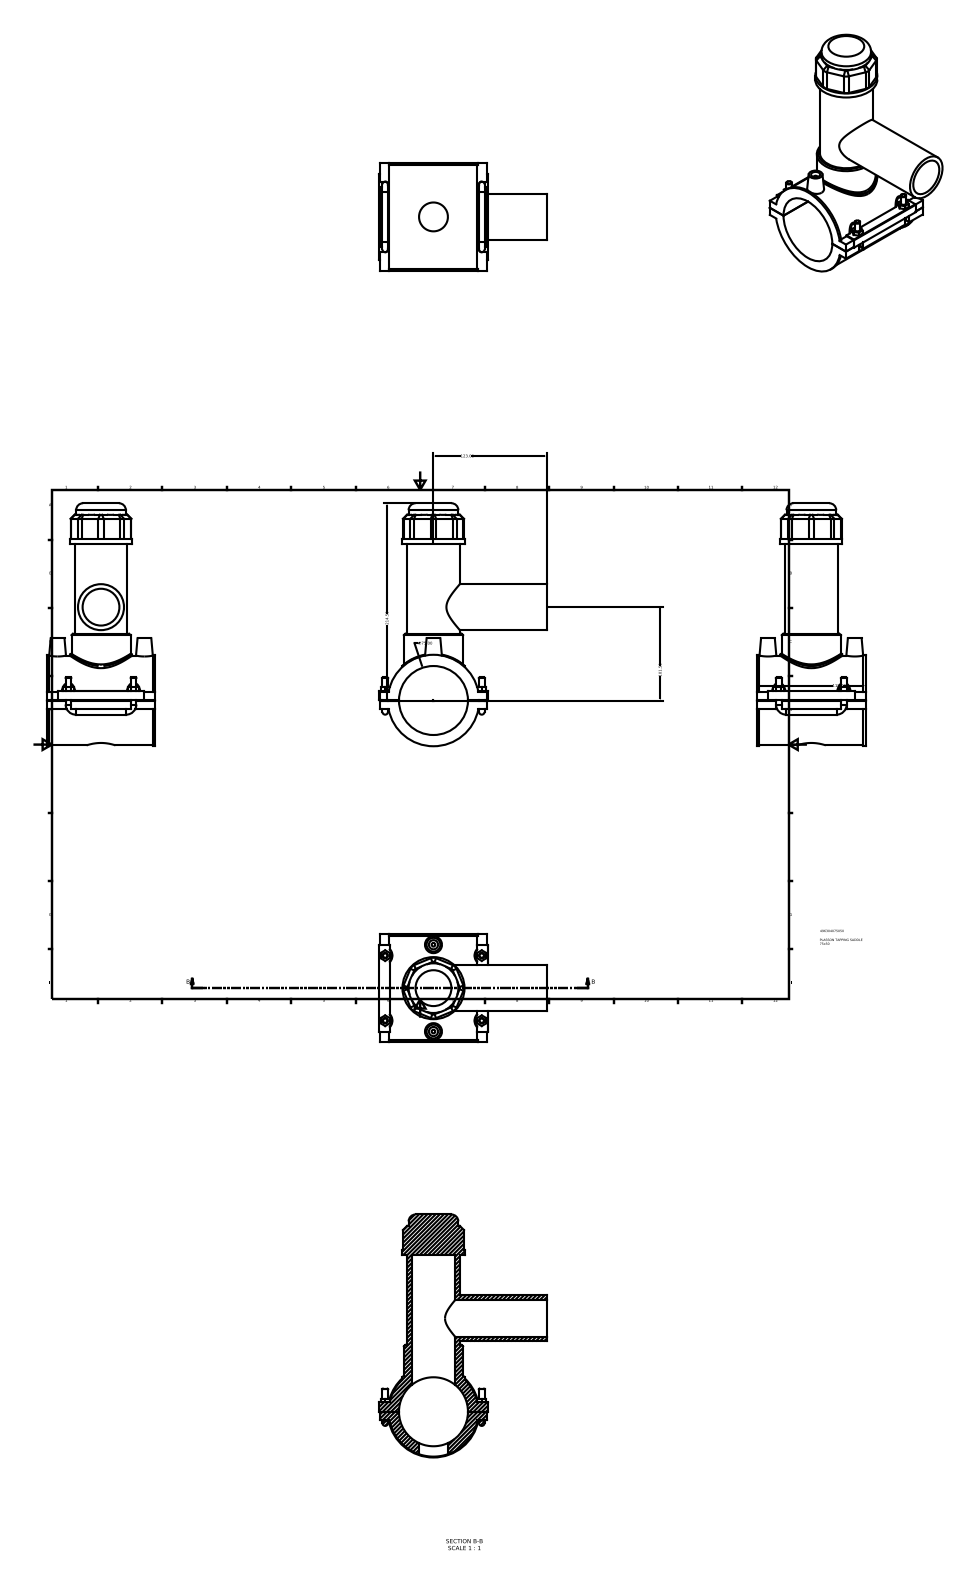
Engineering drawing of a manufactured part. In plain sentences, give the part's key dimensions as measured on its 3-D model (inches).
The part is named "496304075050". Its 3-D file was written by "Autodesk Inventor 2015 (AUTOMOTIVE_DESIGN)". It is 1 solid with 192 faces: 118 planar, 49 cylindrical and 25 other. Overall it measures 10.403 by 7.185 by 4.646 inches. Its volume is 43.13 cubic inches and its surface area 268.4 square inches. Round holes: 2 of diameter 0.394, 1 of diameter 1.235, 1 of diameter 1.575, 1 of diameter 1.86, 1 of diameter 2.953. Round bosses or shafts: 6 of diameter 0.236, 2 of diameter 0.157, 1 of diameter 3.915, 1 of diameter 3.839, 1 of diameter 2.657, 1 of diameter 2.524, 1 of diameter 2.259, 1 of diameter 2.126. Partial cylindrical surfaces (rounded edges, fillets, slot ends): 12 of radius 0.295, 4 of radius 0.118, 1 of radius 0.02, 1 of radius 1.996. The main face-to-face distances are 4.646, 6.705, 6.701, 0.367, 0.371, 0.039, 7.072, 0.778, 0.411, 0.407. The hole center spacings are 1.858, 3.717.
